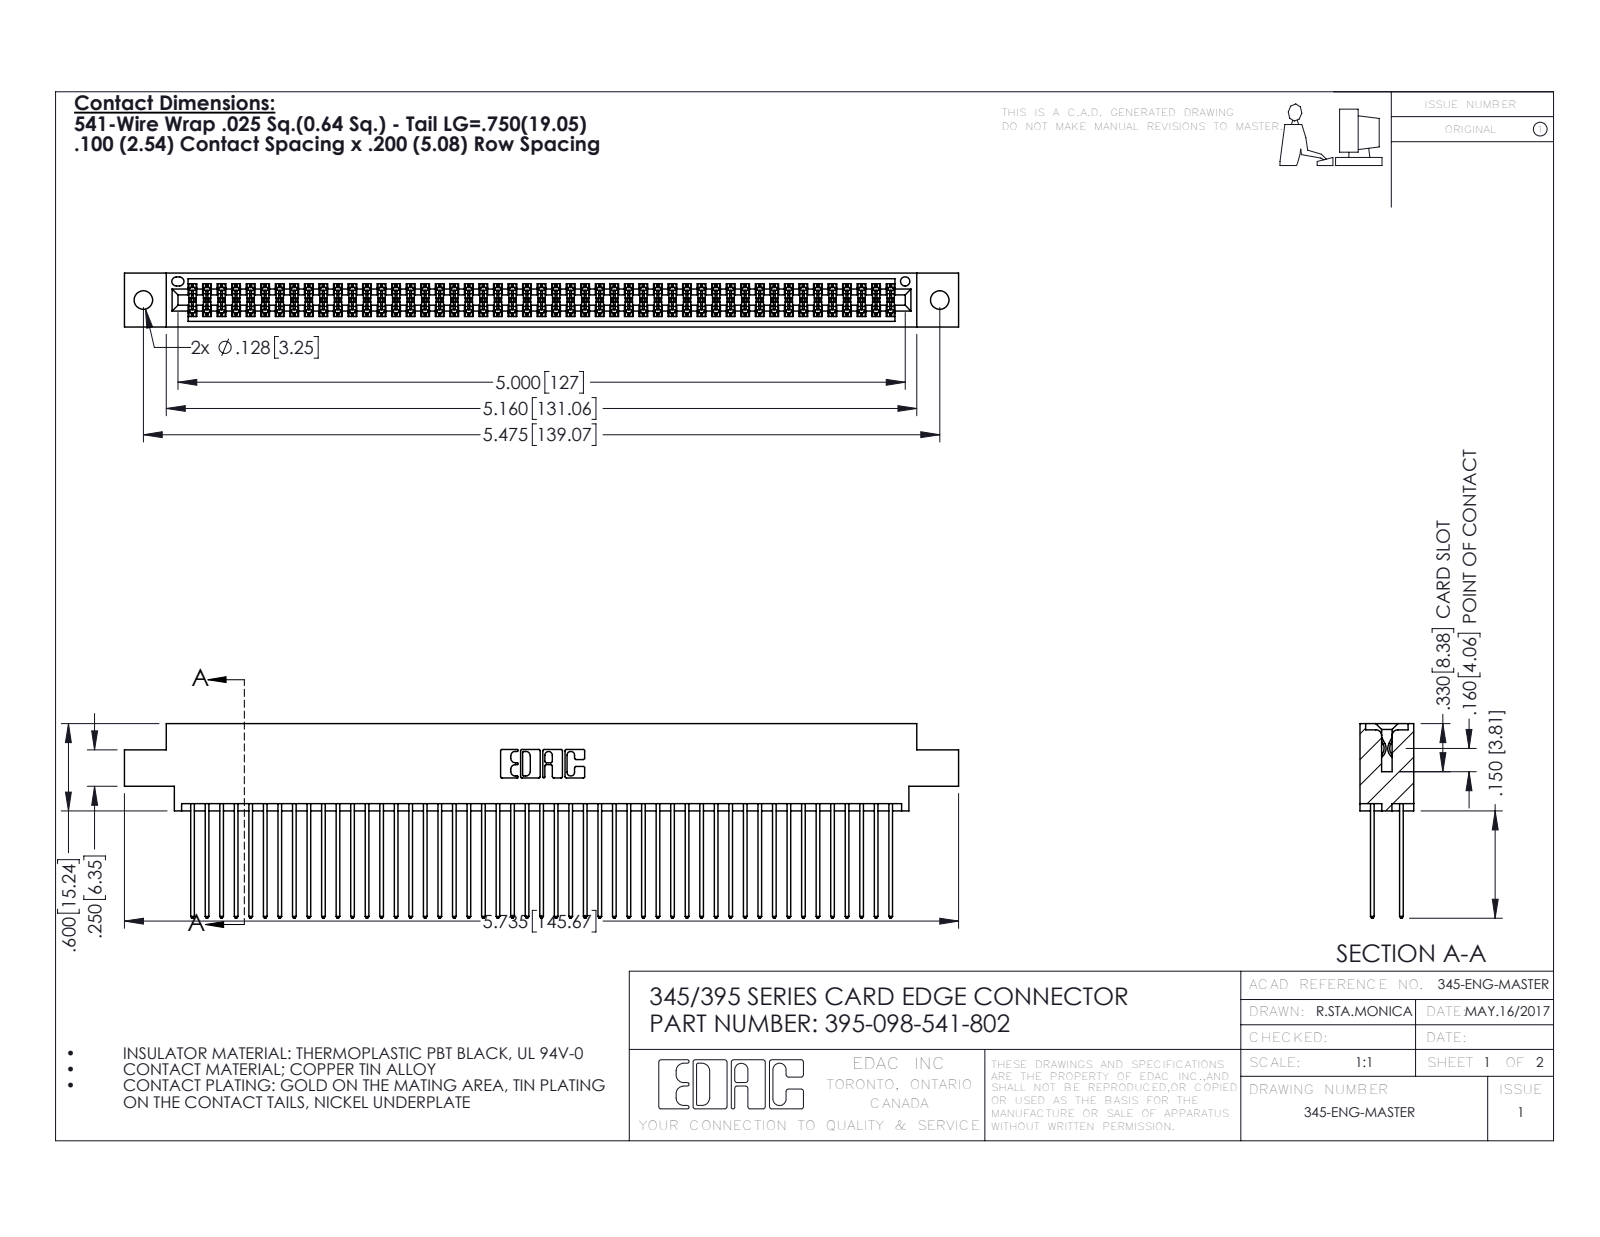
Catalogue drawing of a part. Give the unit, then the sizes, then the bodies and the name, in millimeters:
Units: millimetres
Overall size (bounding box): 145.7 × 34 × 9.4
Round holes (diameter × count): ⌀3.3 ×2, ⌀1.6 ×1
Partial cylindrical surfaces — rounded edges, fillets, slot ends (radius × count): R0.2 ×147, R0.3 ×98, R0.3 ×22, R0.2 ×6, R0.8 ×6, R0.7 ×3, R0.4 ×2, R0.5 ×2
Main face-to-face distances: 7.6, 1.8, 5.1, 2.5, 6.9, 0.6, 5.7, 9.4, 4.4, 3.8
Hole centre spacings: 6.9, 133.1, 139.1
Volume: 14 600 mm³ · Surface area: 24 270 mm²
Bodies: 99 solids, 5030 faces (3318 planar, 1712 cylindrical, 0 other)
Part name (STEP PRODUCT): 345-292-001_345-293-141; 345 Part_0.170 Offset - 0.128 Dia; 395-098-541-802
STEP written by: SolidWorks 2016 (CONFIG_CONTROL_DESIGN)
